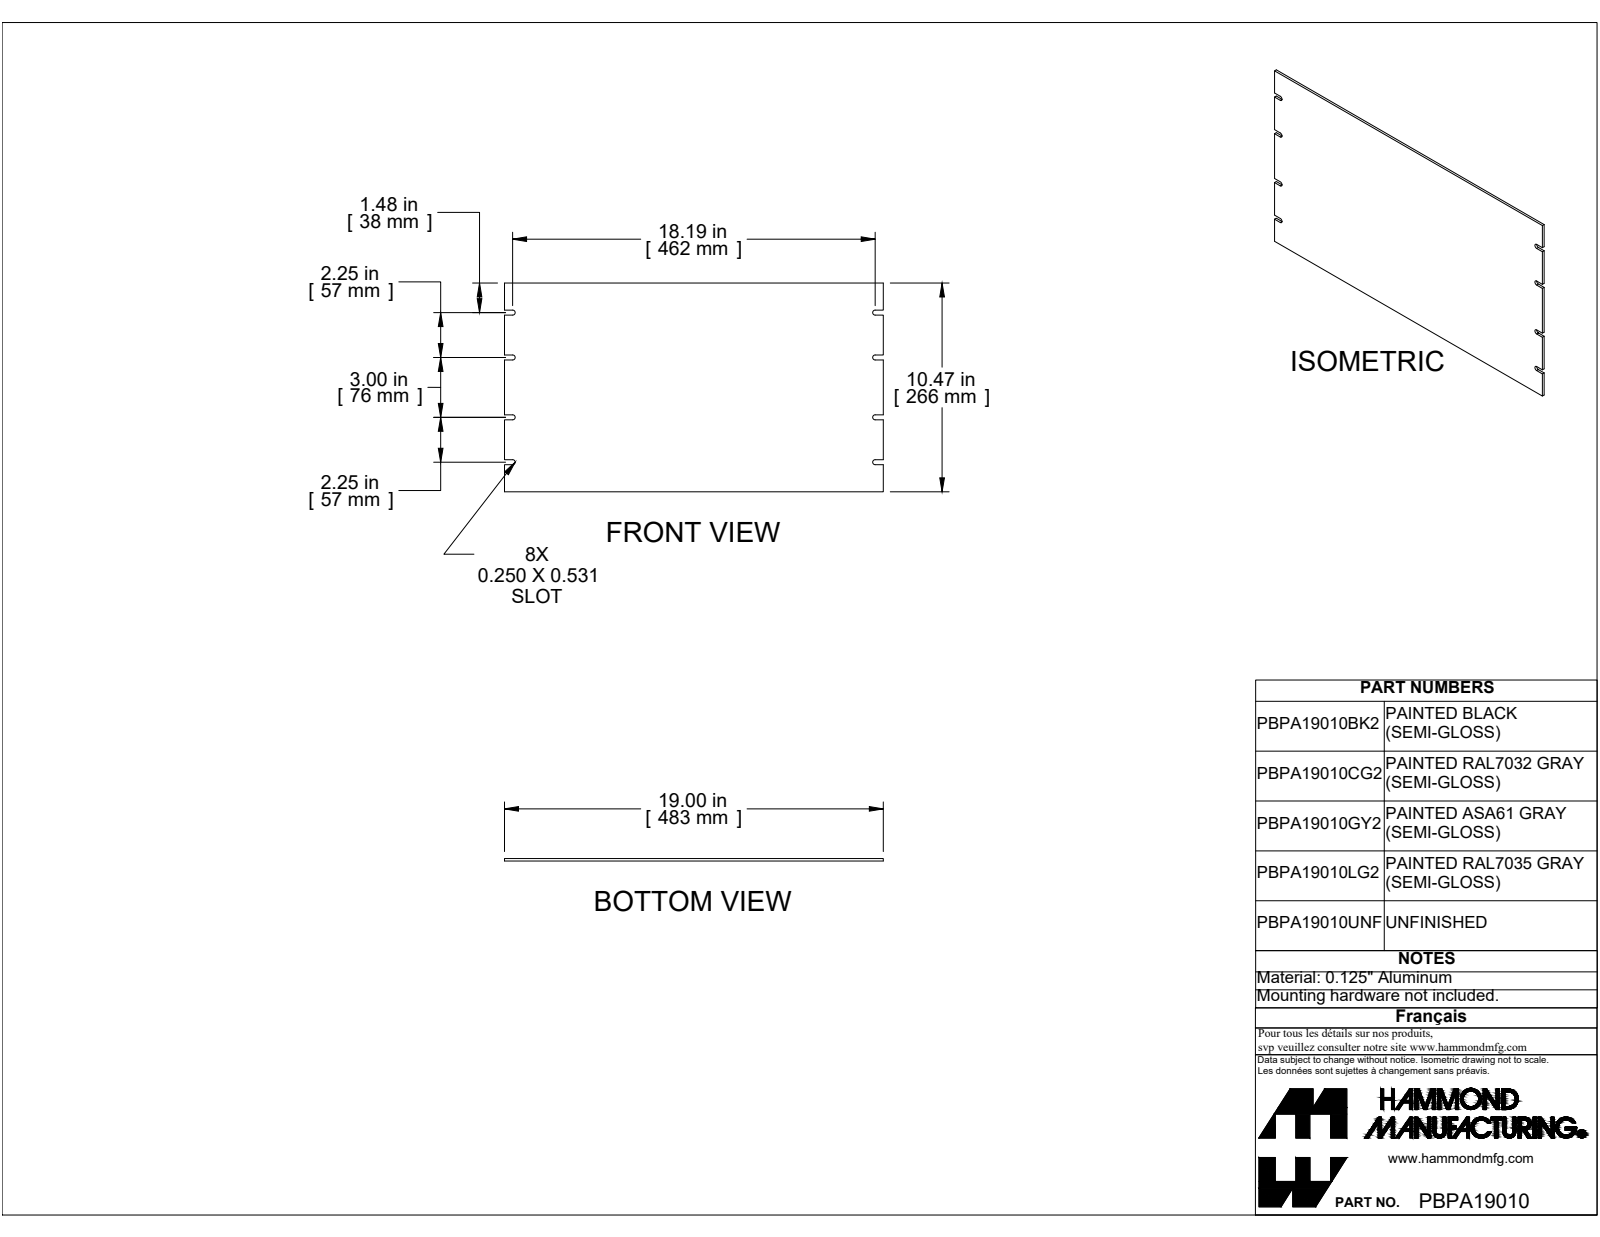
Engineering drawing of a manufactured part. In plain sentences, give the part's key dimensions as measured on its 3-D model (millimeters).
The part is named "PBPA19010BK2". Its 3-D file was written by "SolidWorks 2019 (CONFIG_CONTROL_DESIGN)". It is 1 solid with 38 faces: 30 planar, 8 cylindrical and 0 other. Overall it measures 482.6 by 265.9 by 3.2 millimeters. Its volume is 405 400 cubic millimeters and its surface area 260 700 square millimeters. Partial cylindrical surfaces (rounded edges, fillets, slot ends): 8 of radius 3.2. The main face-to-face distances are 3.2, 265.9, 482.6, 57.2, 133.4, 6.4, 34.5, 40.9, 91.7, 174.2.
